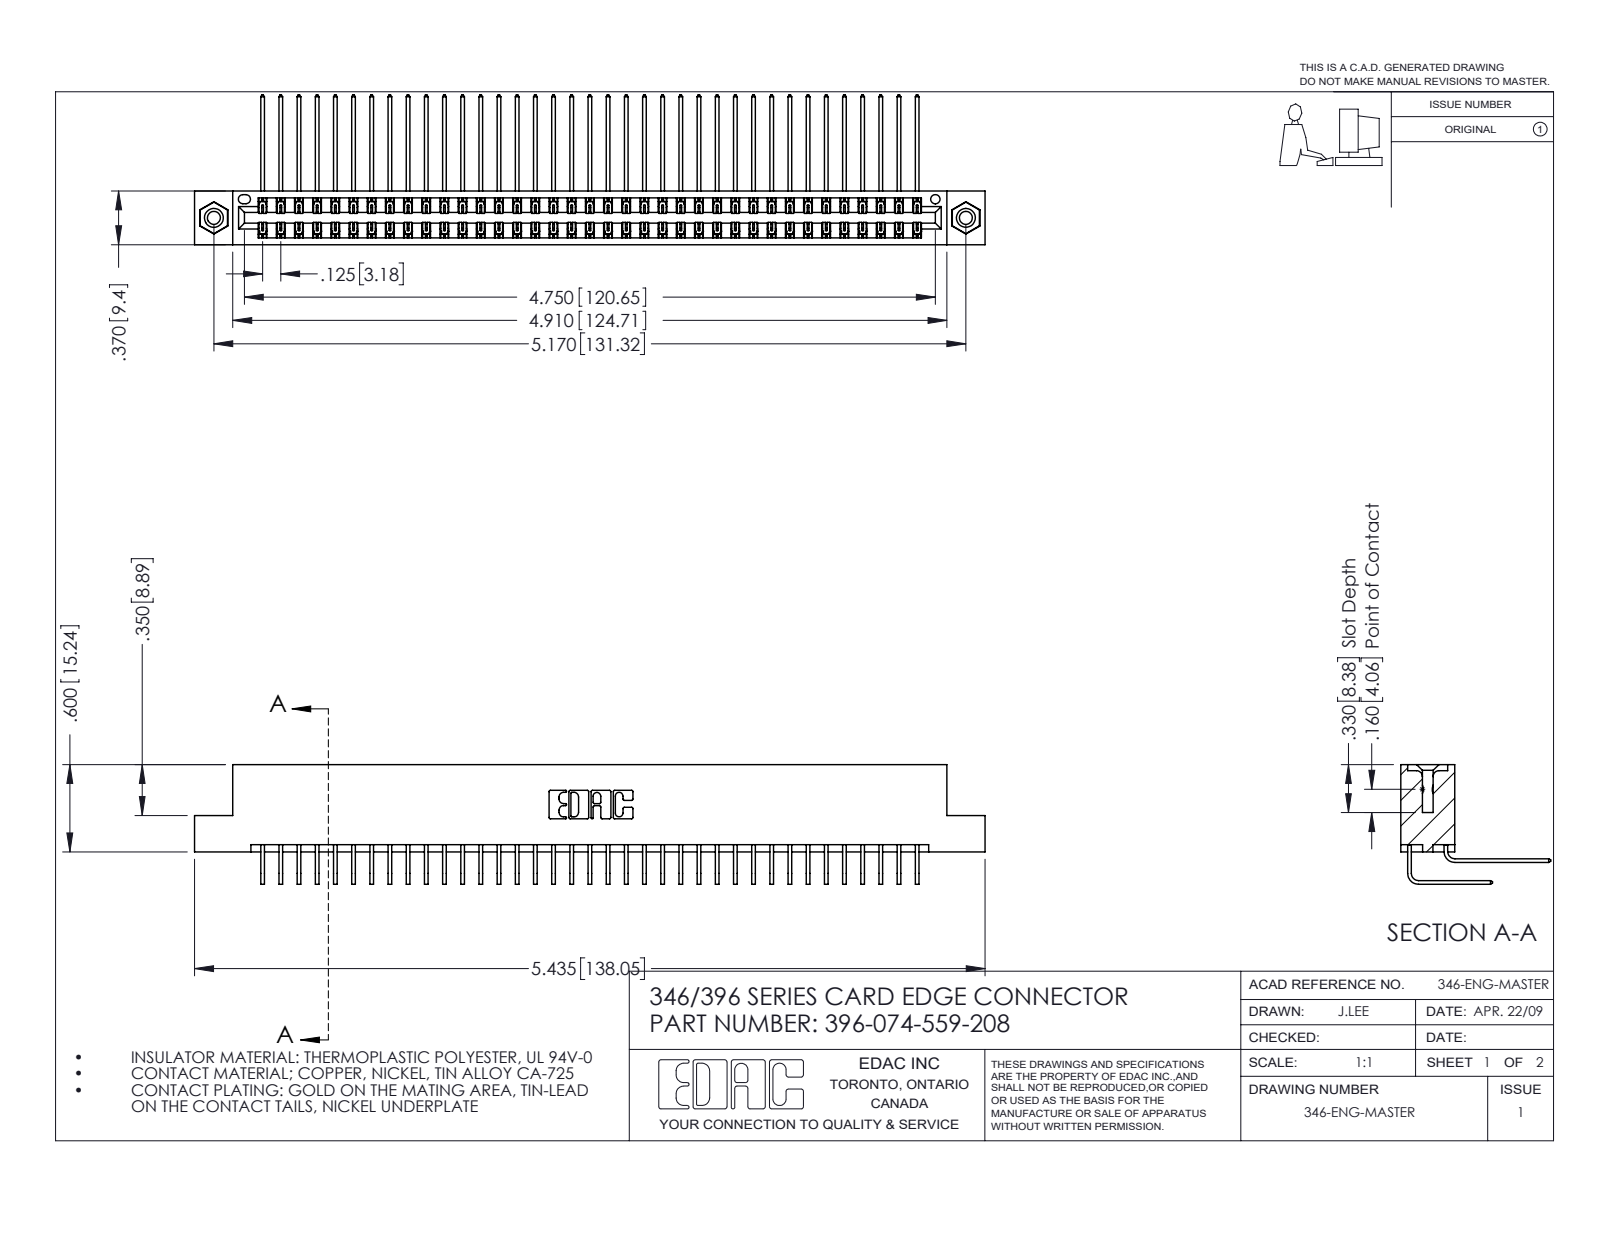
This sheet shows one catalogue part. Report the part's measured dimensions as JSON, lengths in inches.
{"part_name": "345-250-001_345-250-003-102; 345-292-001_559 Tail - 2; 346 Part_Flush Mounting Lugs - 0.156 Dia-TI; 396-074-559-208 (+1 more)", "step_written_by": "SolidWorks 2016 (CONFIG_CONTROL_DESIGN)", "units": "inches", "bodies": {"solids": 77, "faces": 4178, "planar": 2846, "cylindrical": 1316, "other": 16}, "overall_size": [5.435, 1.03, 0.823], "volume_in3": 0.845, "surface_area_in2": 32.58, "round_holes": [[0.089, 2], [0.125, 2], [0.156, 2], [0.064, 1]], "round_bosses_or_shafts": [[0.155, 2]], "partial_cylinders_radius": [[0.006, 111], [0.01, 22], [0.007, 6], [0.031, 6], [0.026, 3], [0.014, 2], [0.022, 2], [0.024, 2]], "face_to_face_distances": [0.048, 0.322, 0.025, 0.37, 0.25, 0.072, 0.298, 0.275, 0.148, 0.222], "hole_center_spacings": [0.246, 4.961, 5.17]}
